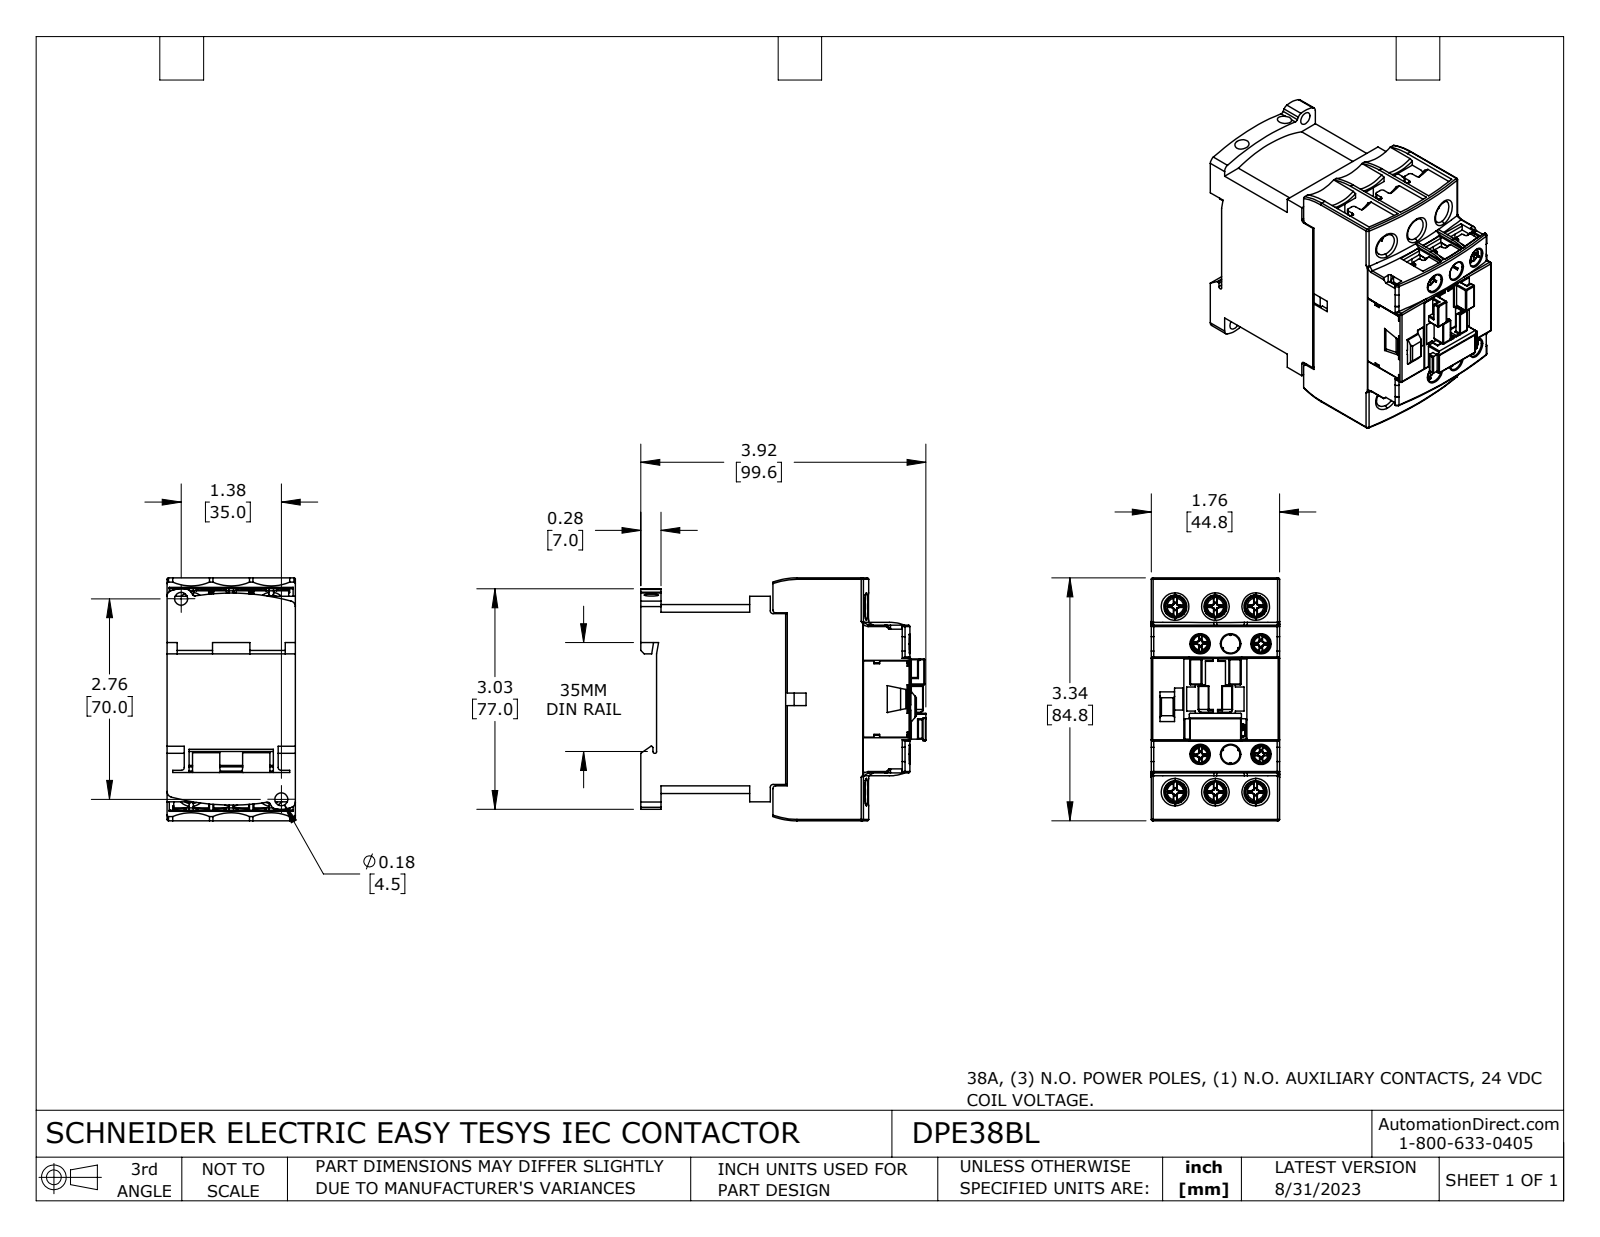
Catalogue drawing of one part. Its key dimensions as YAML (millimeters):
part_name: "DPE38BL"
step_written_by: "SolidWorks 2021 (CONFIG_CONTROL_DESIGN)"
units: millimeters
bodies: {solids: 14, faces: 2629, planar: 1674, cylindrical: 587, other: 368}
overall_size: [99.5, 84.8, 44.8]
volume: 253500
surface_area: 67160
round_holes:
  - {diameter: 6.5, count: 6}
  - {diameter: 8, count: 6}
  - {diameter: 1, count: 2}
  - {diameter: 4.5, count: 2}
  - {diameter: 5, count: 2}
round_bosses_or_shafts:
  - {diameter: 4, count: 8}
  - {diameter: 3.2, count: 6}
  - {diameter: 3.5, count: 4}
  - {diameter: 3.4, count: 4}
  - {diameter: 2.7, count: 4}
  - {diameter: 10, count: 3}
  - {diameter: 0.5, count: 1}
partial_cylinders:
  - {radius: 0.3, count: 51}
  - {radius: 0.5, count: 39}
  - {radius: 0.2, count: 36}
  - {radius: 1, count: 30}
  - {radius: 16, count: 18}
  - {radius: 0.2, count: 15}
  - {radius: 0.8, count: 10}
  - {radius: 2, count: 10}
face_to_face_distances: [44.8, 26.5, 14, 2.4, 24.1, 0.8, 1.2, 1.5, 48.1, 45.6]
hole_center_spacings: [10.6, 14, 40, 66.3, 38.6, 64.8, 14, 14.2]
